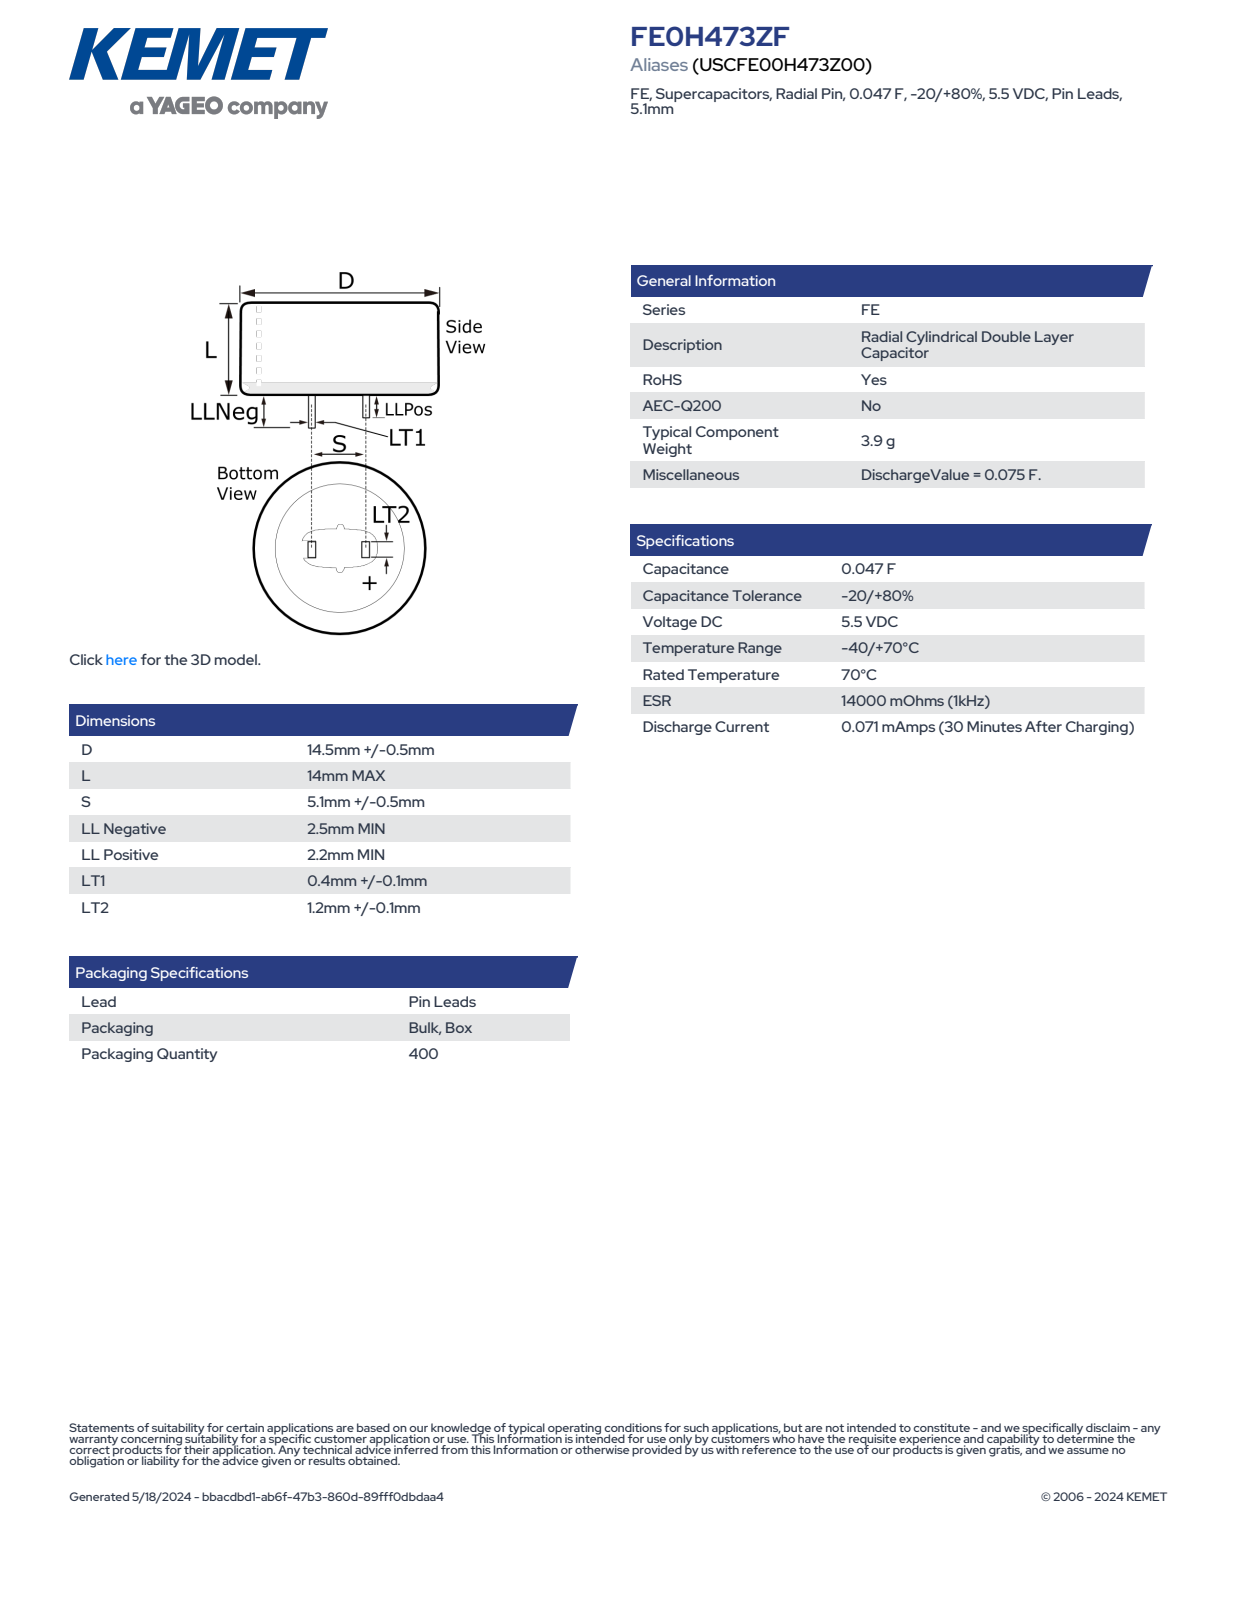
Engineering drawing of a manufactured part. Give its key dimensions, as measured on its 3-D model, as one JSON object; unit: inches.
{"part_name": "CDR_LPLLN_D15L14S5.1LLNEG2.5LLPOS2.2LT10.5LT21.3", "step_written_by": "SolidWorks 2014 (AUTOMOTIVE_DESIGN)", "units": "inches", "bodies": {"solids": 1, "faces": 78, "planar": 70, "cylindrical": 4, "other": 4}, "overall_size": [0.65, 0.591, 0.591], "volume_in3": 0.15, "surface_area_in2": 1.54, "round_bosses_or_shafts": [[0.591, 1]], "partial_cylinders_radius": [[0.296, 1]], "face_to_face_distances": [0.551, 0.02, 0.201, 0.22, 0.181, 0.051, 0.098, 0.65, 0.087, 0.638]}
